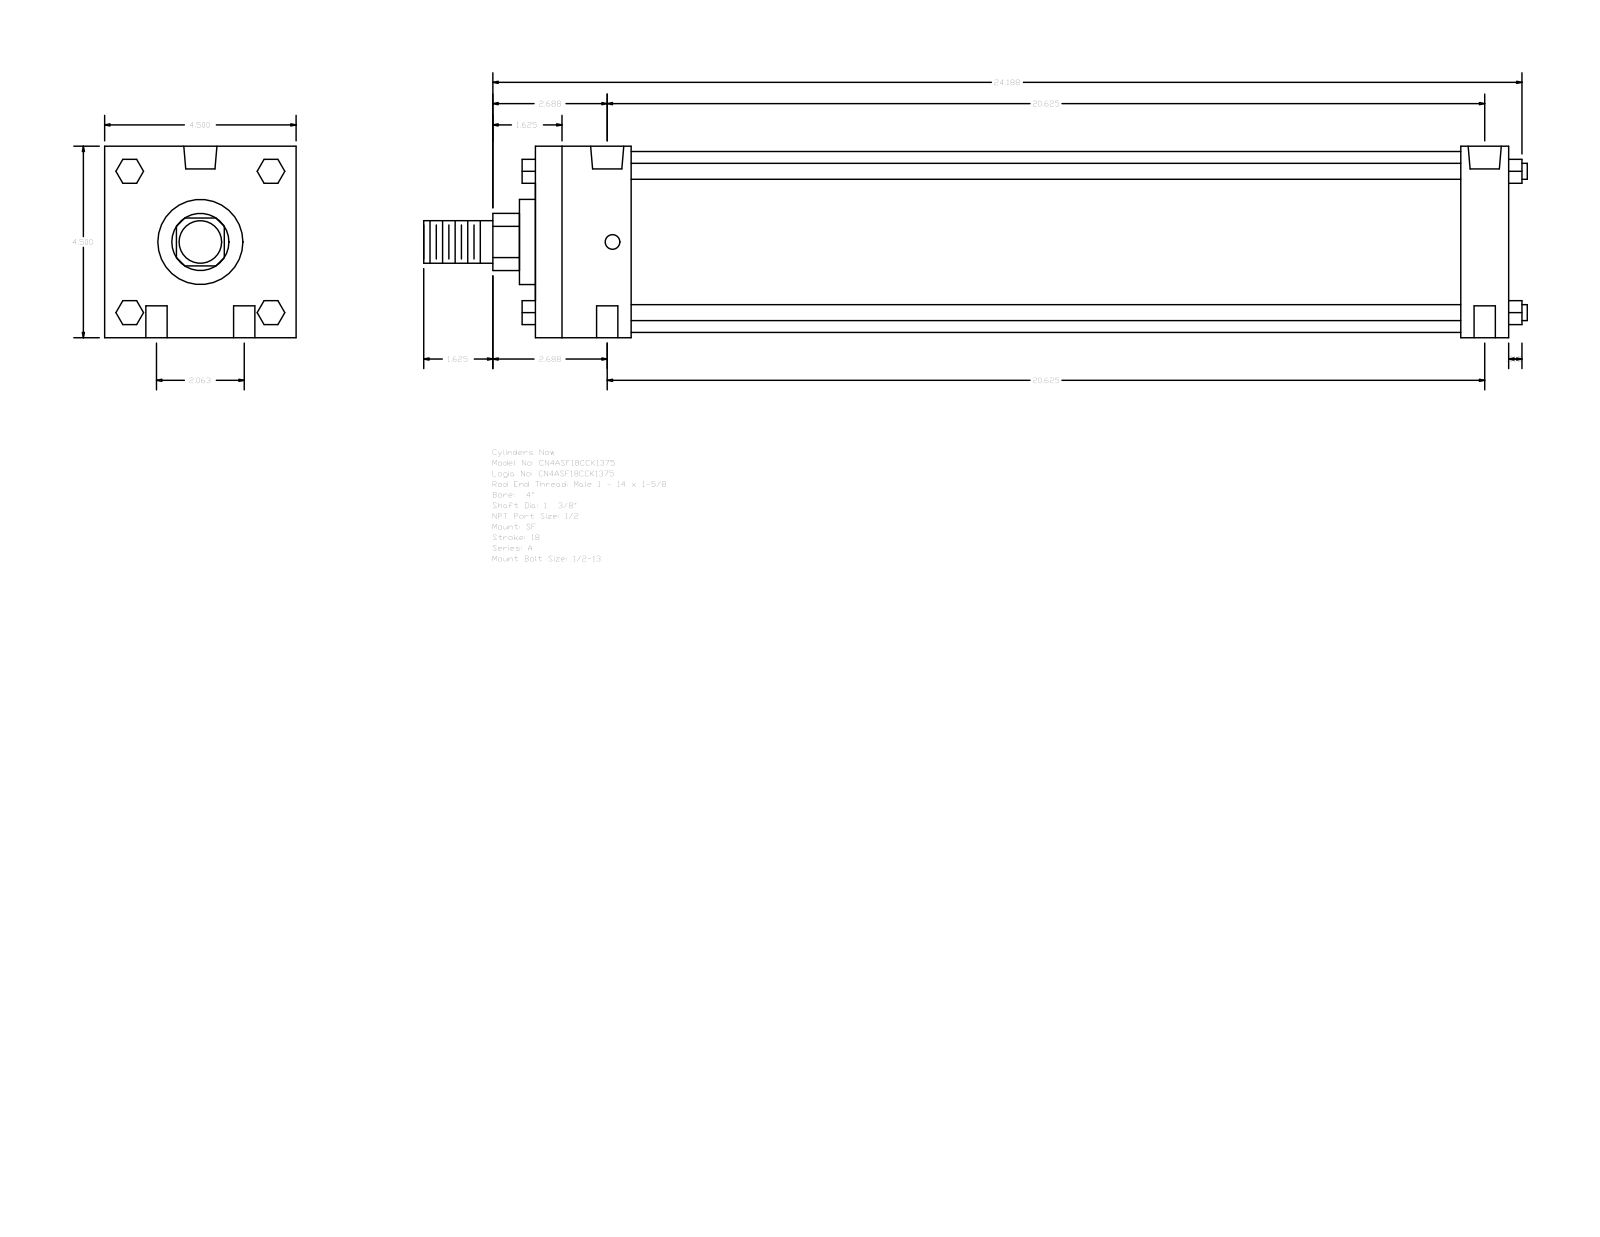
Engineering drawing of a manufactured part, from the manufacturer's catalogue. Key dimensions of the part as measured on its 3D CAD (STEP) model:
Part name (STEP PRODUCT): A_SF__0400_1.375
STEP written by: GSSL Pune (CONFIG_CONTROL_DESIGN)
Units: millimetres
Bodies: 0 solids, 124 faces (94 planar, 30 cylindrical, 0 other)
Overall size (bounding box): 658.81 × 114.3 × 114.3
Round holes (diameter × count): ⌀12.7 ×4, ⌀8.73 ×2, ⌀19.77 ×2
Round bosses / shafts (diameter × count): ⌀9.53 ×4, ⌀107.95 ×1, ⌀50.8 ×1, ⌀34.92 ×1, ⌀25.4 ×1
Partial cylindrical surfaces — rounded edges, fillets, slot ends (radius × count): R17.06 ×1
Main face-to-face distances: 114.3, 581.02, 57.15, 552.45, 28.57, 495.3, 523.87, 66.67, 14.29, 9.52
Hole centre spacings: 26.19, 524.53, 523.88, 52.38, 526.49, 517.52
